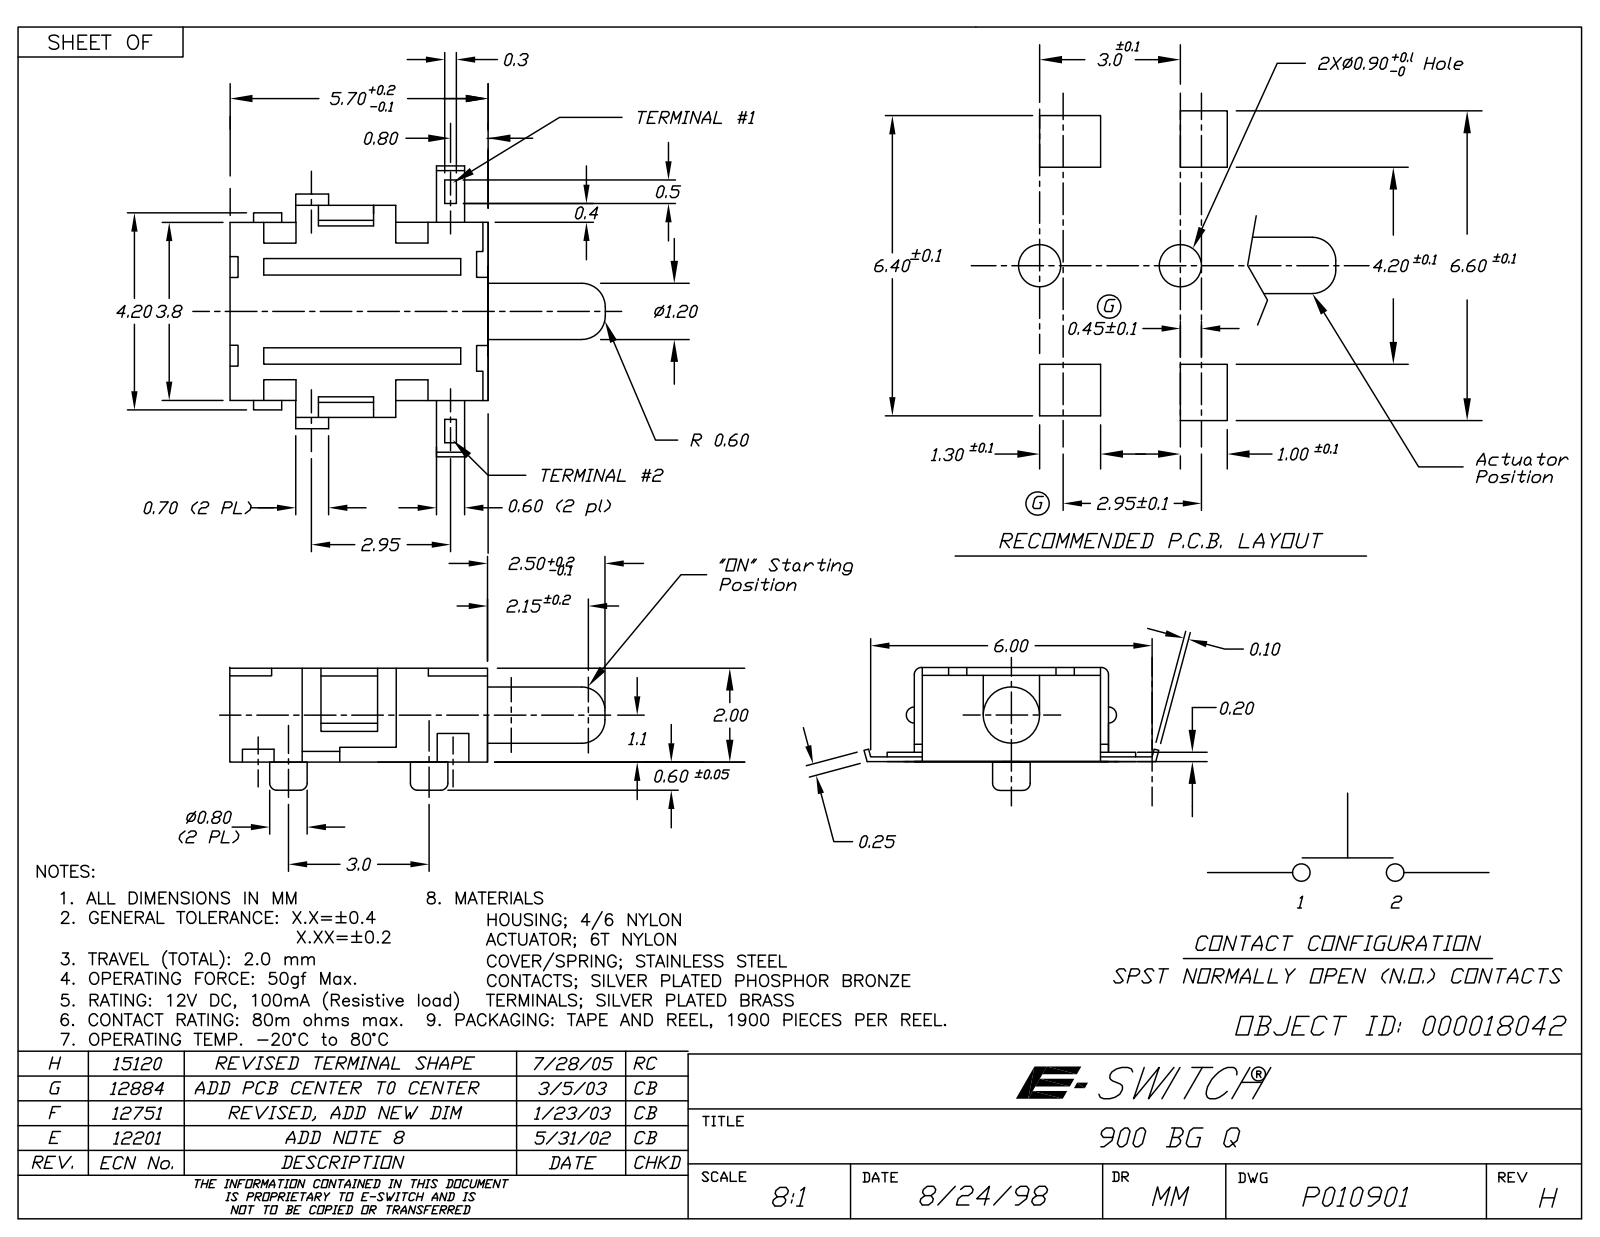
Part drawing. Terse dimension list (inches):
name: P:\\E-Switch Secure\\3D_MODELS_STP_FORMAT\\900BGQ.stp
written by: ACIS (CONFIG_CONTROL_DESIGN)
unit: in
bodies: 1 solid, 134 faces (113 planar, 14 cylindrical, 7 other)
size: 0.325 × 0.256 × 0.102
volume: 0.002 in³; area: 0.29 in²
holes: 4× ⌀0.01
bosses: 2× ⌀0.031, 1× ⌀0.047
rounds: 4× R0.008, 1× R0.025
face distances: 0.079, 0.067, 0.014, 0.059, 0.071, 0.051, 0.055, 0.144, 0.02, 0.063
hole spacings: 0.079, 0.138, 0.159
